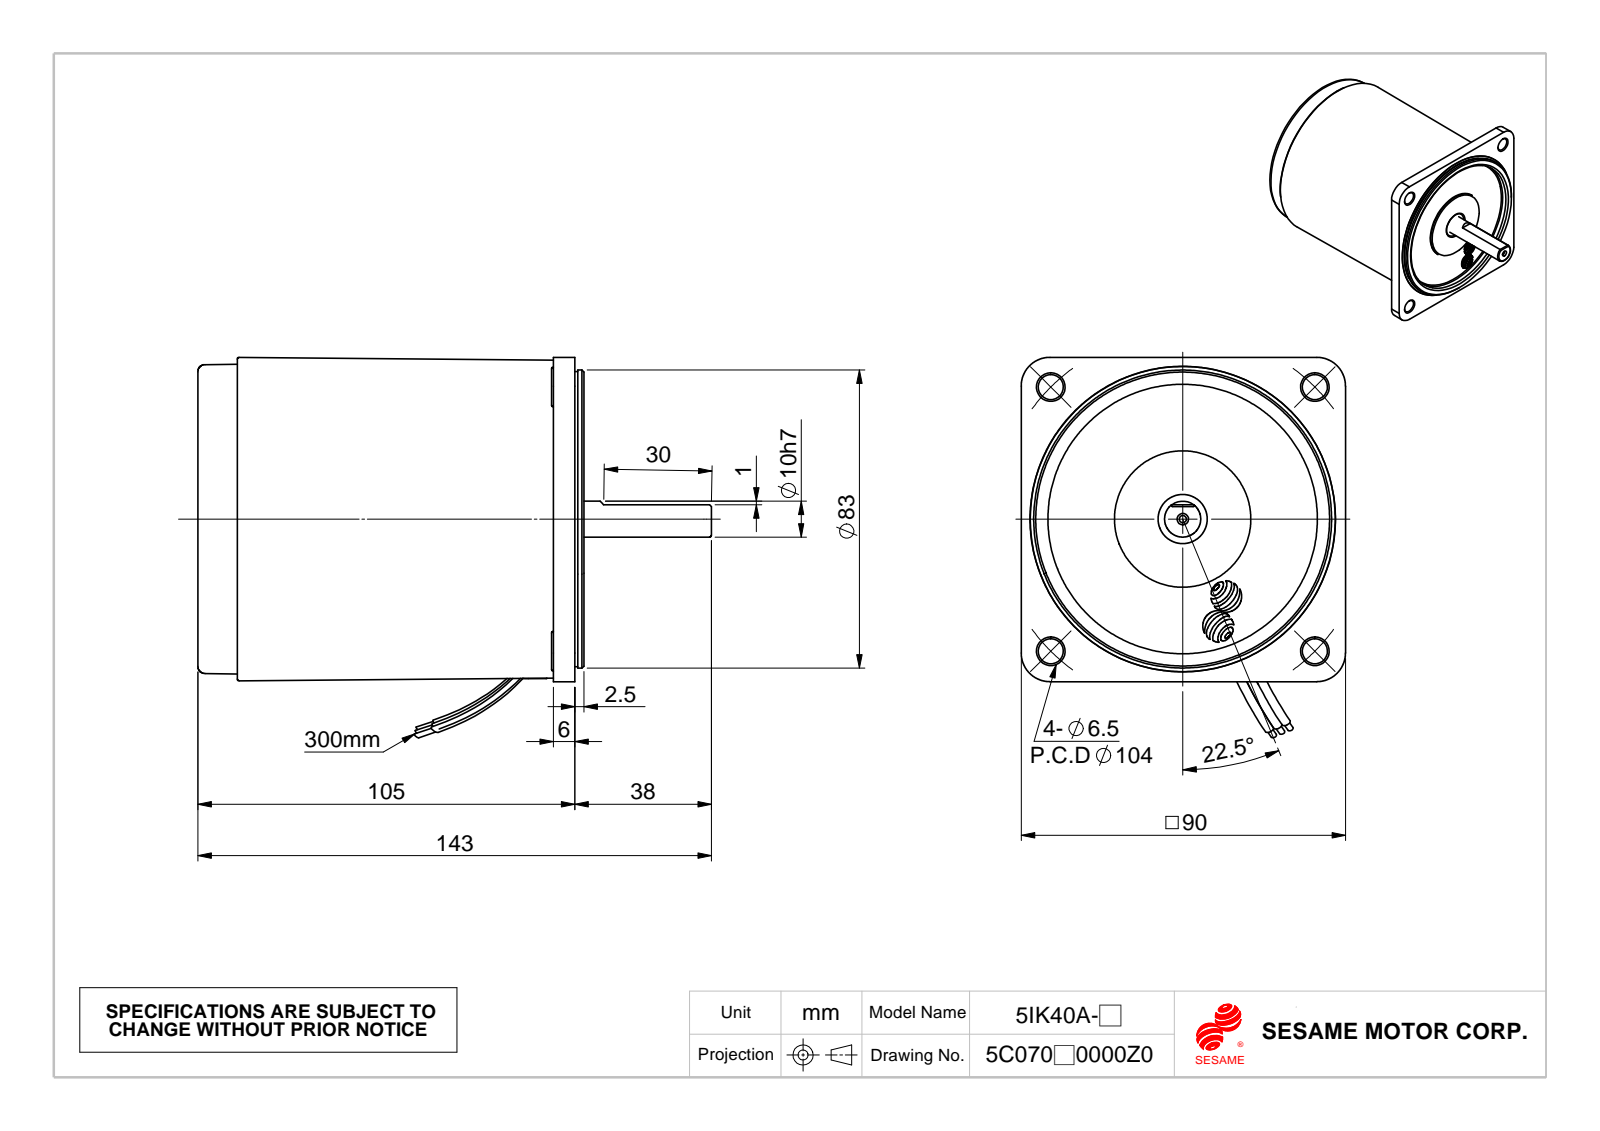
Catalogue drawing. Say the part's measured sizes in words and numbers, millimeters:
The part is named "線扣; M540; 40A". Its 3-D file was written by "SolidWorks 2010 (CONFIG_CONTROL_DESIGN)". It is 7 solids with 364 faces: 75 planar, 195 cylindrical and 94 other. Overall it measures 143 by 105.88 by 90.3 millimeters. Its volume is 664 402 cubic millimeters and its surface area 66 054 square millimeters. Round holes: 4 of diameter 7, 1 of diameter 2, 1 of diameter 2.5, 1 of diameter 7.2, 1 of diameter 9.5, 1 of diameter 13.7, 1 of diameter 26, 1 of diameter 58.1, 1 of diameter 75, 1 of diameter 84.4, 1 of diameter 85. Round bosses or shafts: 1 of diameter 84.22, 1 of diameter 84.15, 1 of diameter 83, 1 of diameter 82.2, 1 of diameter 38, 1 of diameter 10, 1 of diameter 9.3. Partial cylindrical surfaces (rounded edges, fillets, slot ends): 8 of radius 0.25, 8 of radius 0.78, 8 of radius 1.5, 8 of radius 1.66, 8 of radius 2.92, 4 of radius 0.2, 4 of radius 0.58, 4 of radius 2.58. The main face-to-face distances are 1, 102.5, 0.9, 103.5, 2.5, 101.5, 102.4, 103.4, 1.5, 105. The hole center spacings are 52, 73.54, 104.
